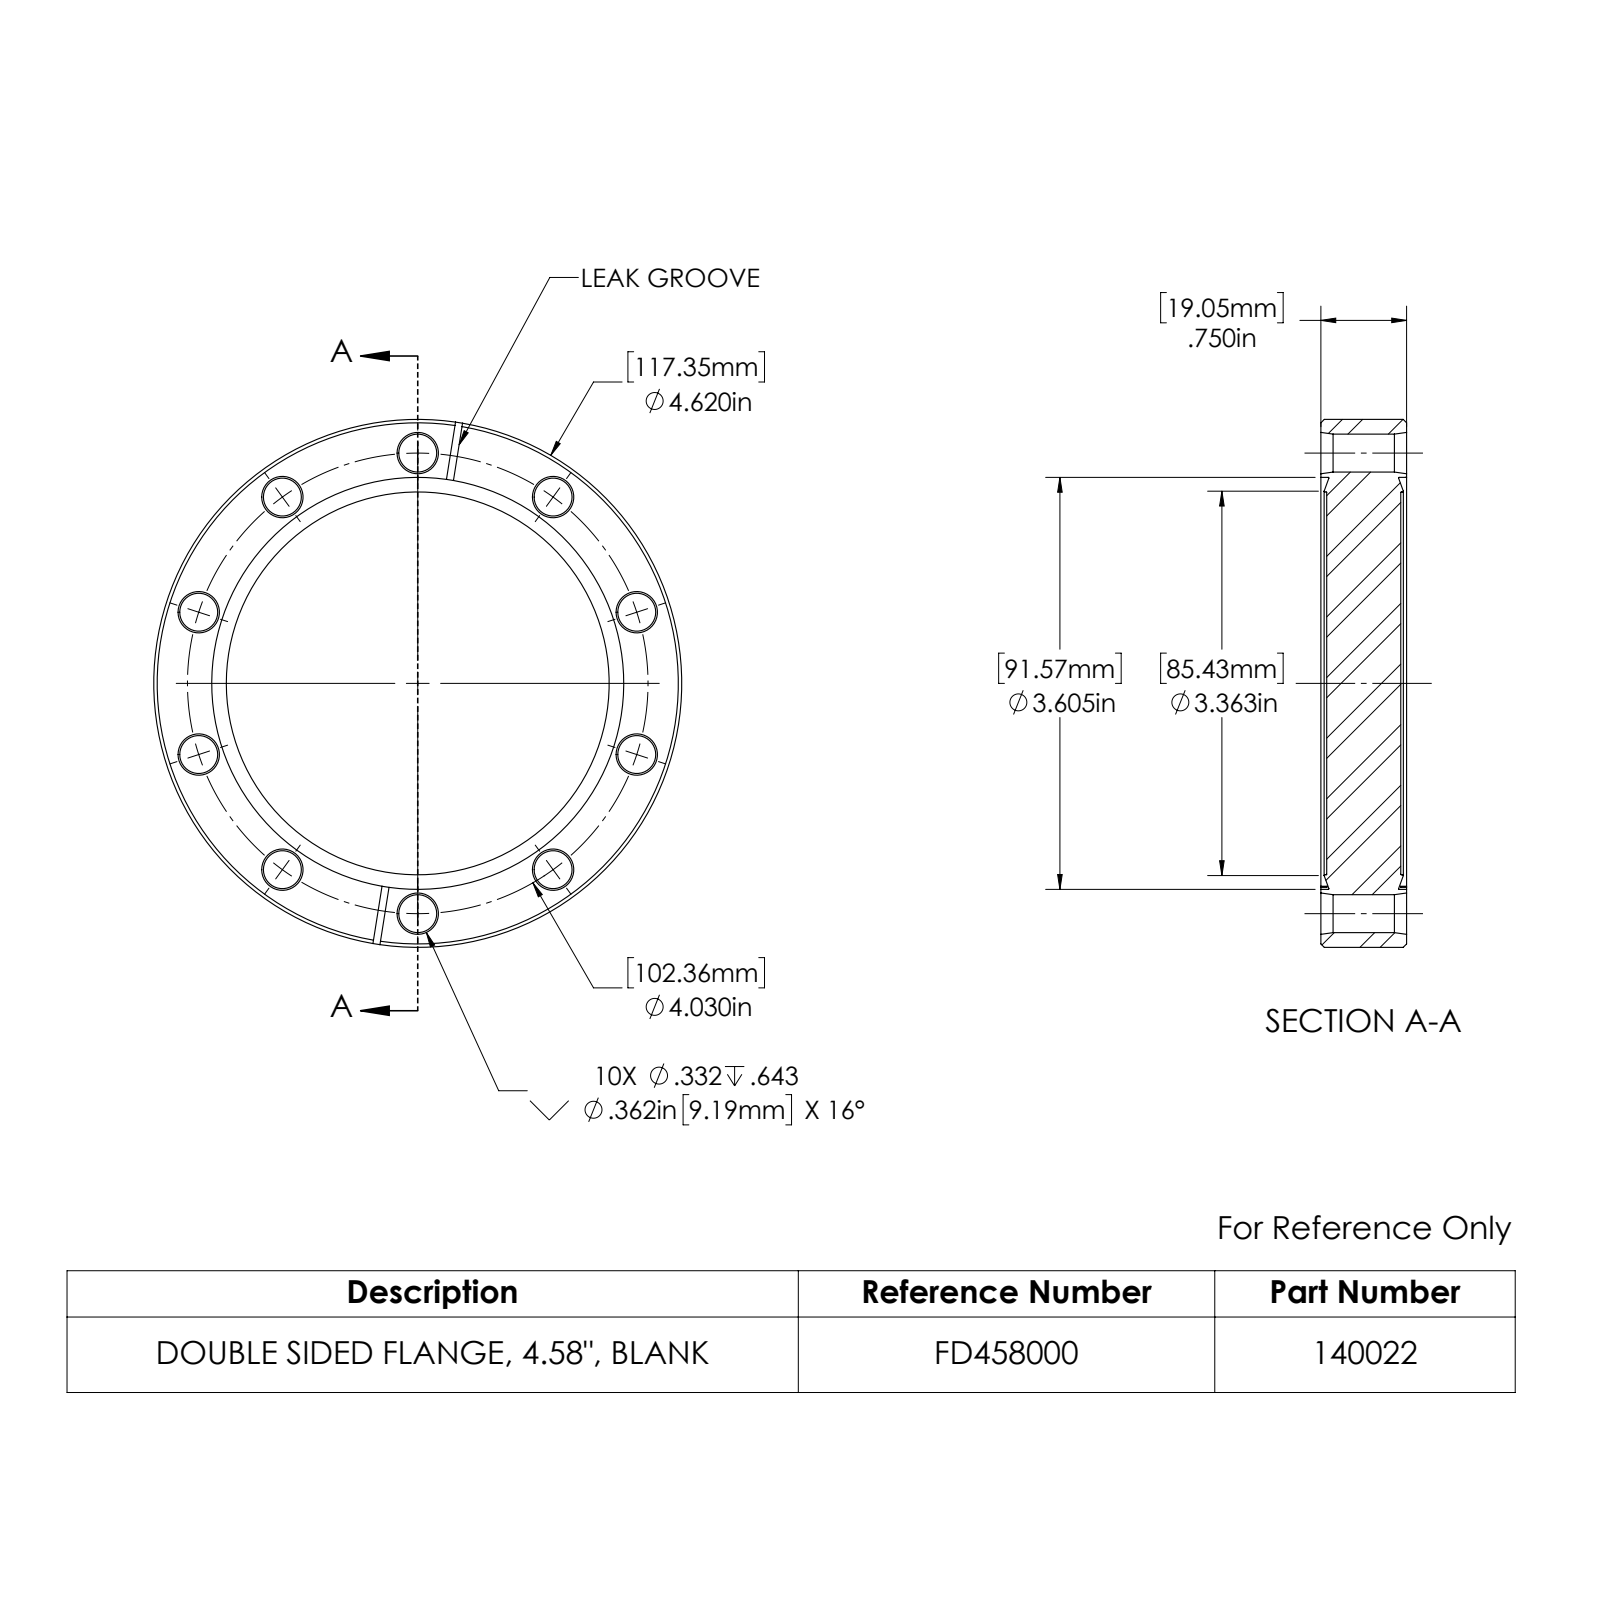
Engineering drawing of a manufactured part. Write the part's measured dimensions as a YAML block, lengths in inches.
part_name: "140022_A"
step_written_by: "SolidWorks 2022 (CONFIG_CONTROL_DESIGN)"
units: inches
bodies: {solids: 1, faces: 110, planar: 14, cylindrical: 34, other: 62}
overall_size: [4.62, 4.62, 0.75]
volume: 10.84
surface_area: 52.3
round_holes:
  - {diameter: 0.332, count: 10}
  - {diameter: 3.35, count: 1}
  - {diameter: 3.605, count: 1}
round_bosses_or_shafts:
  - {diameter: 4.62, count: 1}
partial_cylinders:
  - {radius: 1.25, count: 4}
face_to_face_distances: [0.051, 0.699, 0.648, 0.75, 0.062, 0.065, 0.06]
hole_center_spacings: [1.246, 2.015, 3.261, 3.833, 1.245, 2.015, 2.369, 2.369]
